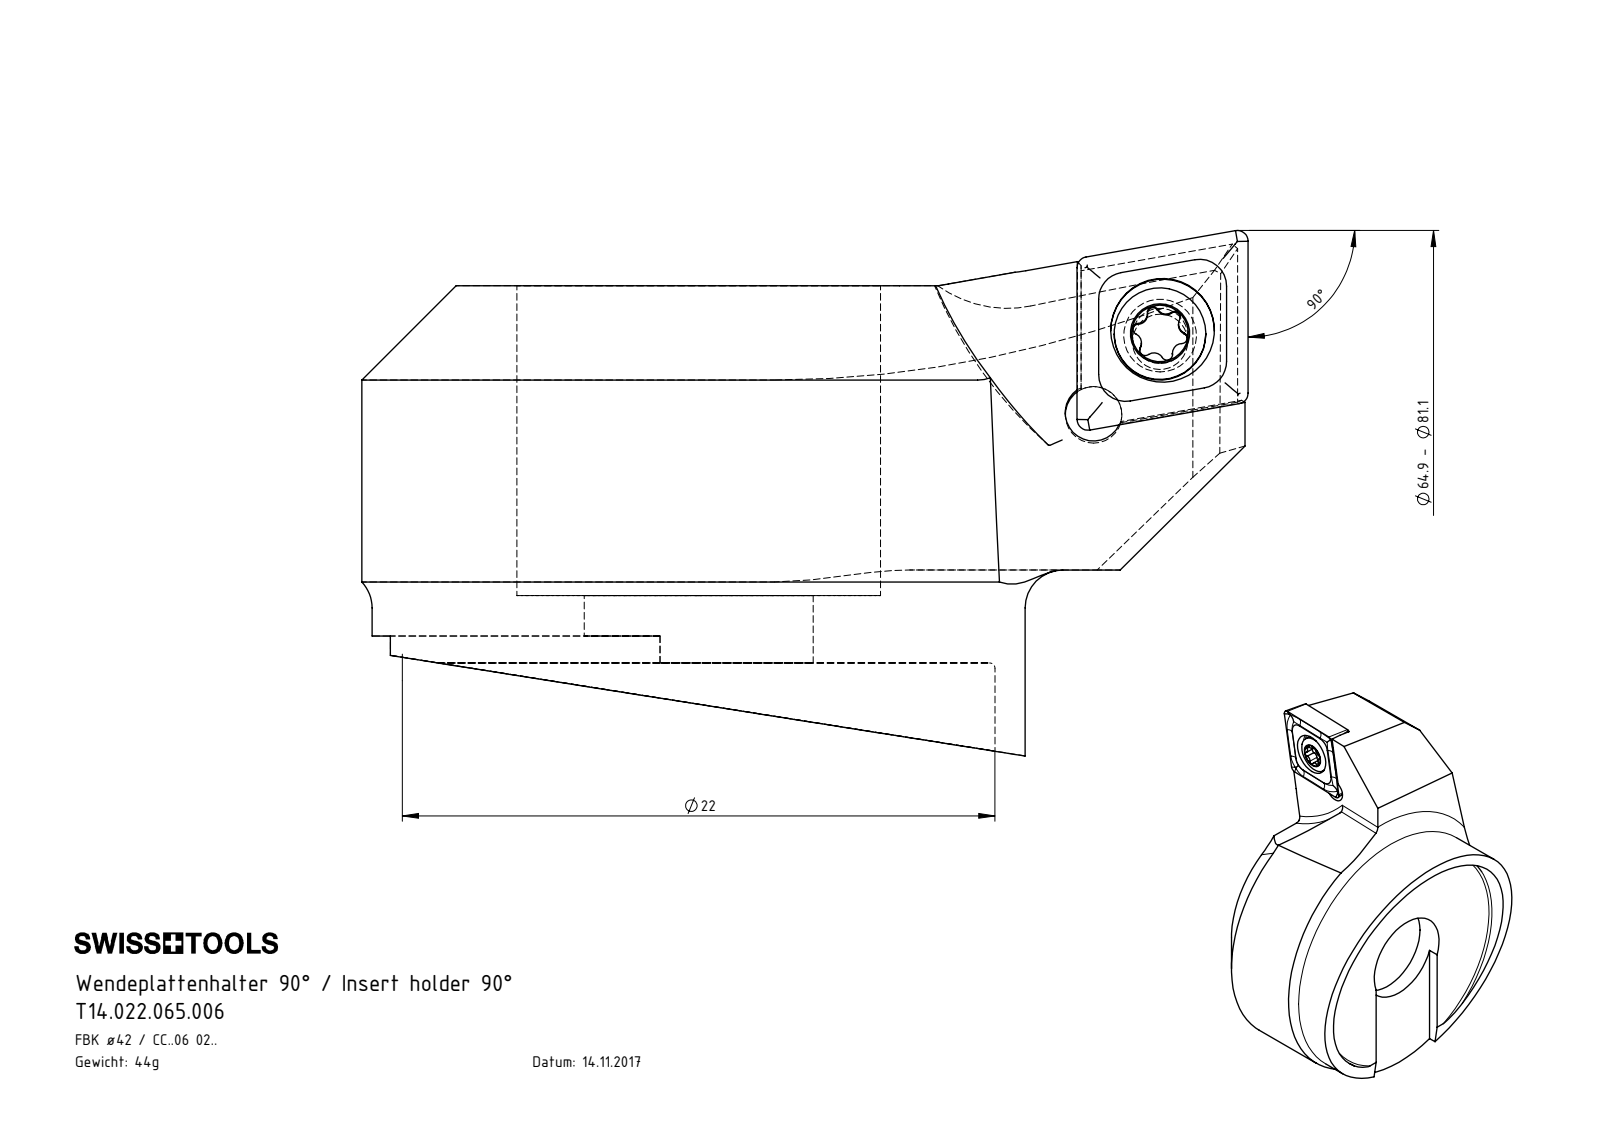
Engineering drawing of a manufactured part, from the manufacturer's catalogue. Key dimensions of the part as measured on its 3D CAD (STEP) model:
Part name (STEP PRODUCT): WCA-ER2.001.006_A; F42.WCA.001.016; CCMT060204; F42-WCA.001.016_A_fertigbearbeitet
STEP written by: SolidWorks 2017 (AUTOMOTIVE_DESIGN)
Units: millimetres
Bodies: 3 solids, 105 faces (39 planar, 27 cylindrical, 39 other)
Overall size (bounding box): 32.9 × 25 × 19.5
Volume: 5 498 mm³ · Surface area: 3 122 mm²
Round holes (diameter × count): ⌀2.05 ×1, ⌀2.1 ×1, ⌀2.8 ×1, ⌀3.85 ×1, ⌀8.5 ×1, ⌀13.5 ×1
Round bosses / shafts (diameter × count): ⌀24.25 ×1, ⌀3.4 ×1, ⌀2.5 ×1
Partial cylindrical surfaces — rounded edges, fillets, slot ends (radius × count): R0.21 ×6, R0.36 ×5, R0.5 ×2, R0.36 ×1, R5 ×1, R11 ×1, R12.5 ×1, R16 ×1
Main face-to-face distances: 14, 11.5, 2.5, 13, 1.5, 1, 2.28, 10.55, 0.95, 2.45
Hole centre spacings: 3.84, 4
